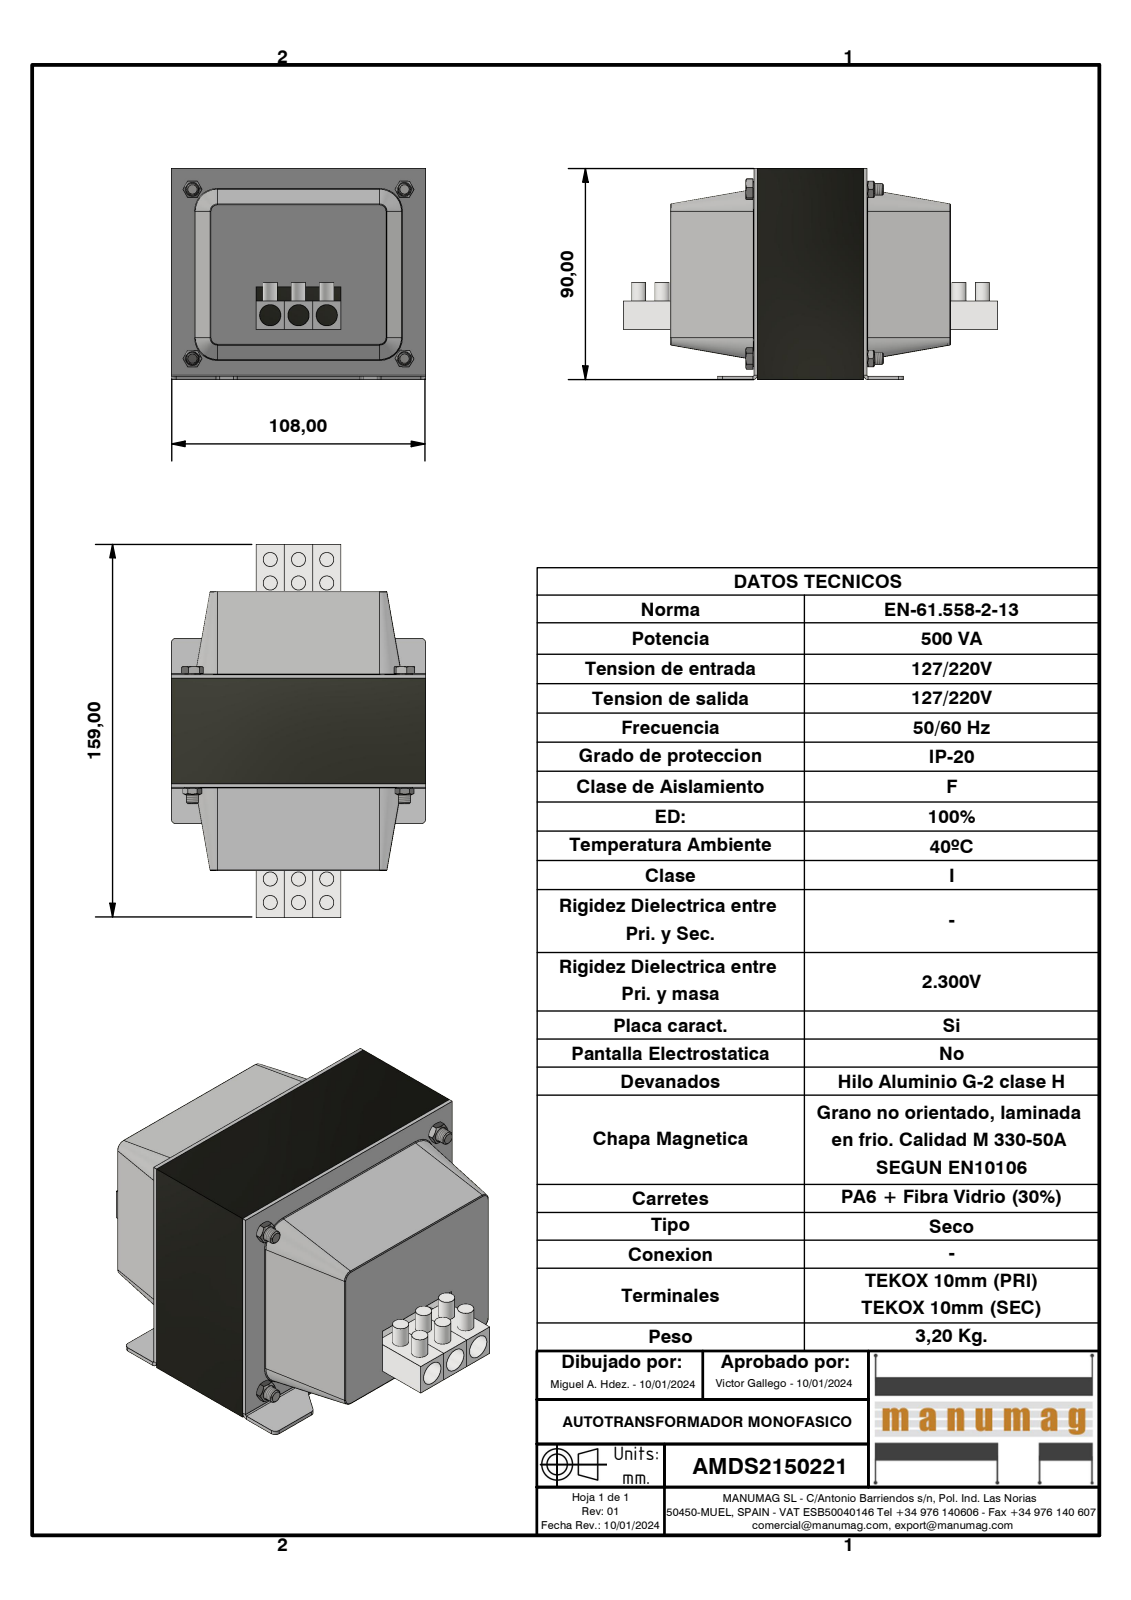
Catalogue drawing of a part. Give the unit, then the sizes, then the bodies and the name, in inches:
Units: inches
Overall size (bounding box): 6.26 × 4.252 × 3.543
Round holes (diameter × count): ⌀0.128 ×4, ⌀0.197 ×4, ⌀0.22 ×4, ⌀0.354 ×3
Round bosses / shafts (diameter × count): ⌀0.236 ×12, ⌀0.264 ×4, ⌀0.18 ×4
Partial cylindrical surfaces — rounded edges, fillets, slot ends (radius × count): R0.015 ×16, R0.079 ×14, R0.02 ×2
Main face-to-face distances: 0.059, 1.398, 3.228, 0.709, 2.835, 1.772, 3.543, 3.131, 1.417, 3.169
Hole centre spacings: 0.472, 1.489, 1.915, 2.359, 2.476, 2.754, 2.835, 3.079
Volume: 24.09 in³ · Surface area: 221.7 in²
Bodies: 17 solids, 352 faces (194 planar, 78 cylindrical, 80 other)
Part name (STEP PRODUCT): AMDS2150221; DIN 933 - M5 x 55; DIN 934 - M4 x 0,7; TAPA RC36 VENTANA 3 ELEMENTOS 10 CON FICHAS (+4 more)
STEP written by: Autodesk Inventor 2023 (AUTOMOTIVE_DESIGN)
